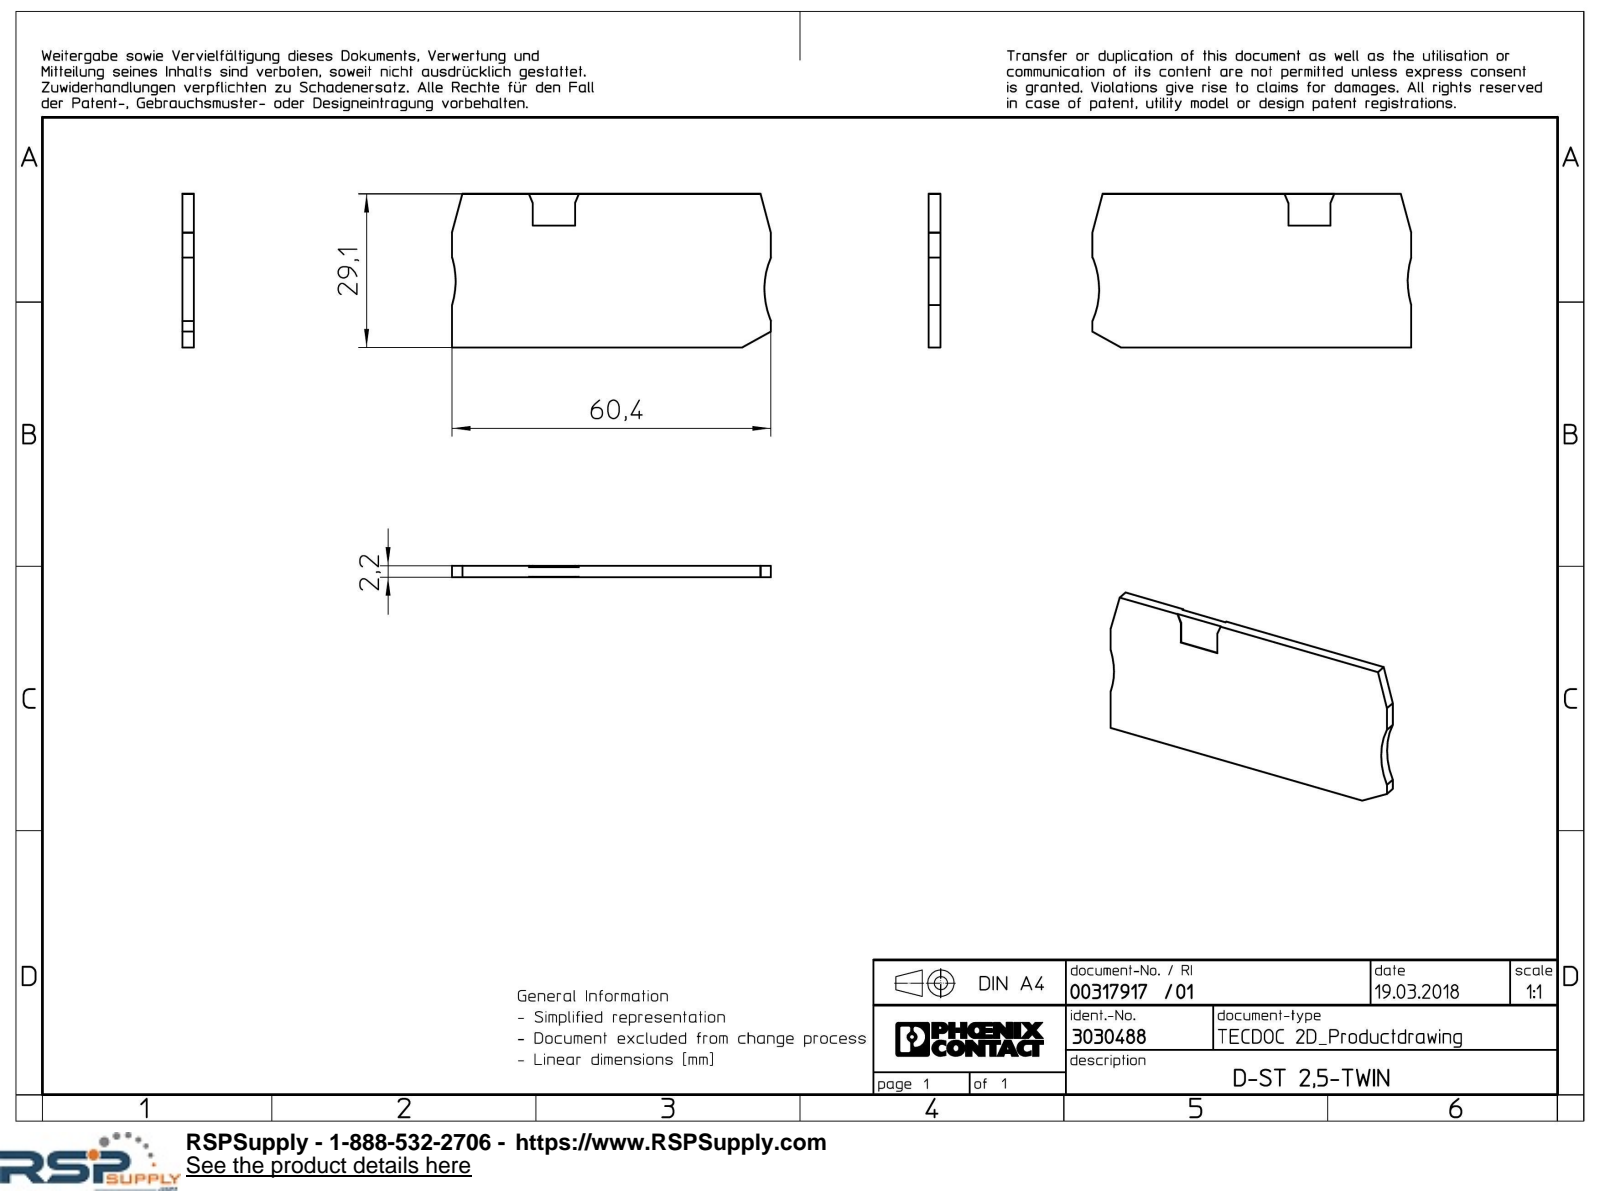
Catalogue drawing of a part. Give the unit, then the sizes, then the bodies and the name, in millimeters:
Units: millimetres
Overall size (bounding box): 60.4 × 29.05 × 2.2
Partial cylindrical surfaces — rounded edges, fillets, slot ends (radius × count): R15 ×2
Main face-to-face distances: 2.2, 29.05, 1.9, 2.1, 1.8, 60.4, 23.05, 6, 23.3, 37.1
Volume: 3 760 mm³ · Surface area: 3 822 mm²
Bodies: 1 solid, 25 faces (23 planar, 2 cylindrical, 0 other)
Part name (STEP PRODUCT): D-ST_2.5-TWIN-SELECT
STEP written by: Creo Elements/Direct Modeling 18.1I 14-Aug-2016 (C) Parametric Technology GmbH (AUTOMOTIVE_DESIGN)
